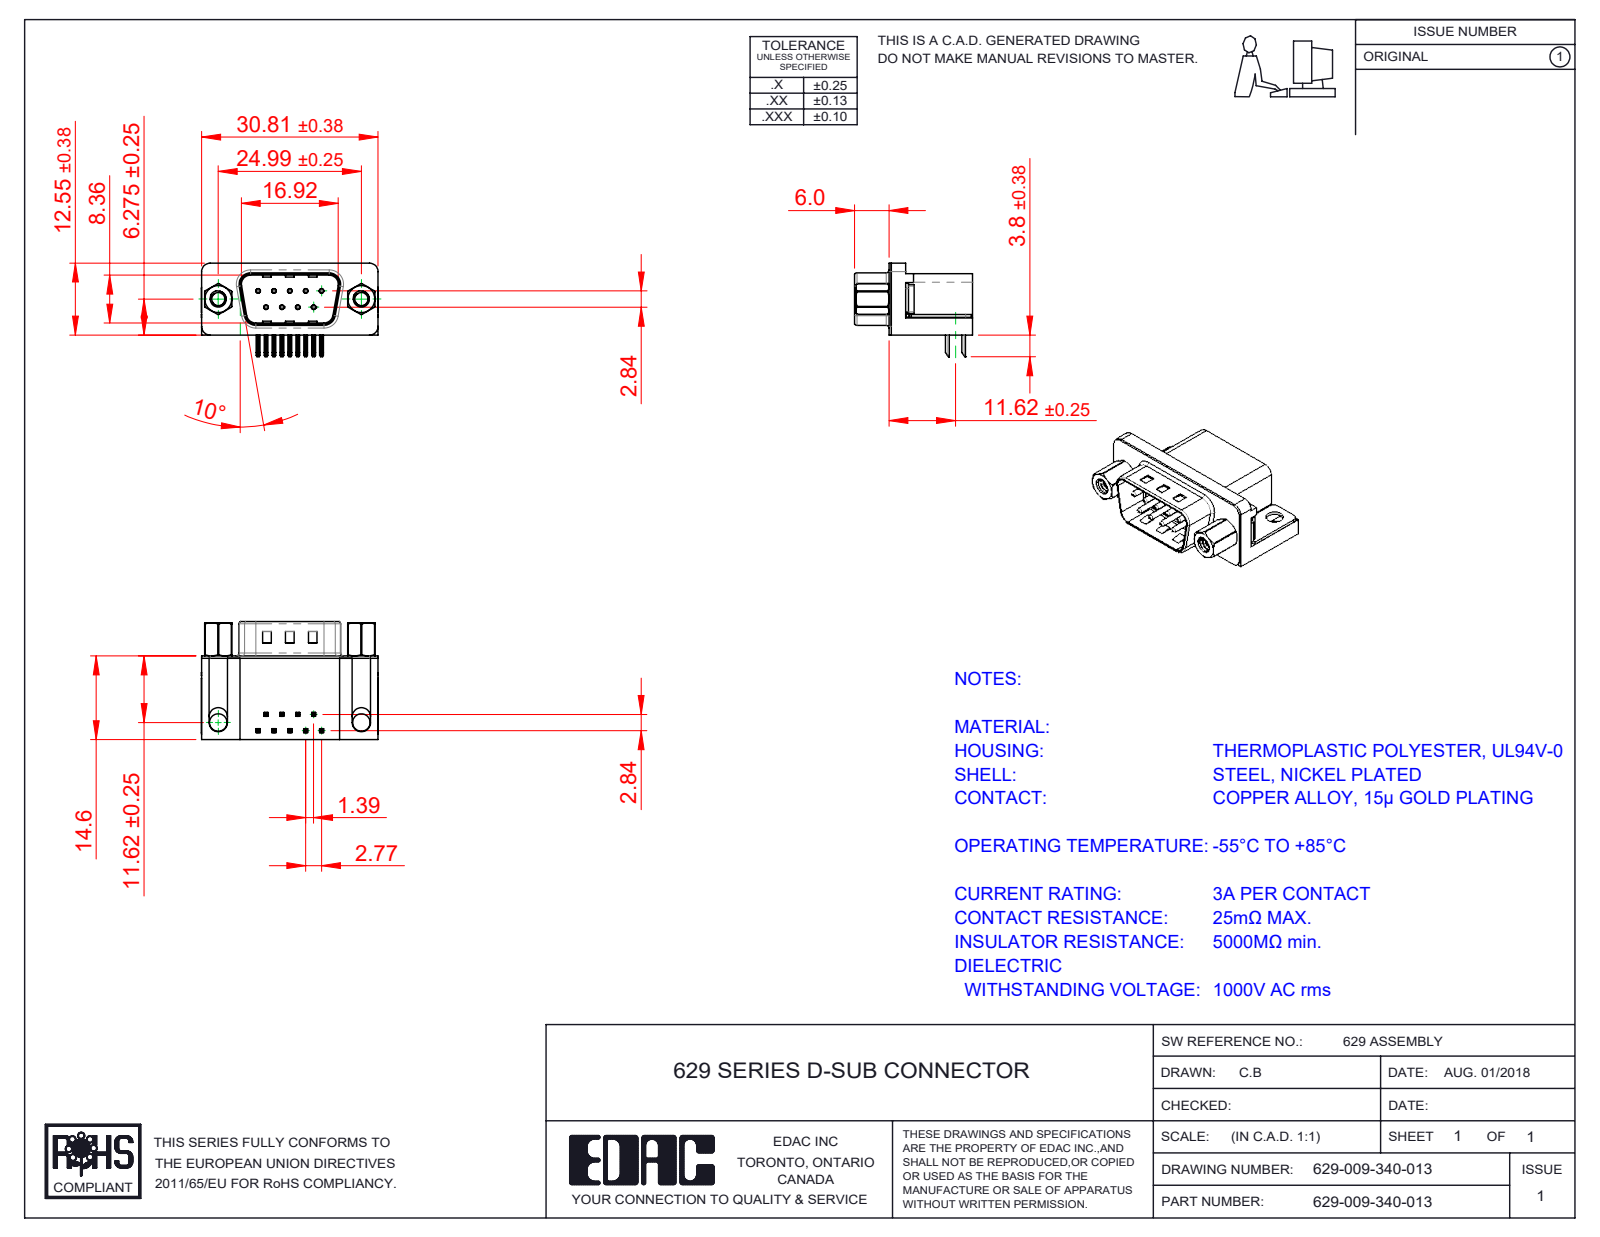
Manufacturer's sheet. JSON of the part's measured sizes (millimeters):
{"part_name": "629 Housing_09 Socket; 629 4-40 Hex Standoff 5; 629 Shell_09 Socket; 629 4-40 Threaded Rivet (+4 more)", "step_written_by": "SolidWorks 2020 (CONFIG_CONTROL_DESIGN)", "units": "millimeters", "bodies": {"solids": 17, "faces": 1115, "planar": 593, "cylindrical": 387, "other": 135}, "overall_size": [30.89, 20.6, 16.35], "volume_mm3": 3930, "surface_area_mm2": 5210, "round_holes": [[0.35, 9], [0.8, 9], [2.26, 2], [2.29, 2], [3.05, 2], [4, 2], [4.8, 2], [5, 2]], "round_bosses_or_shafts": [[0.75, 9], [4.9, 2], [4.75, 2], [3.9, 2], [2.79, 2]], "partial_cylinders_radius": [[0.25, 44], [0.12, 18], [1, 16], [0.5, 9], [1.5, 8], [1.6, 8], [0.9, 4], [2, 4]], "face_to_face_distances": [0.4, 14.2, 14.6, 10.35, 0.5, 11.7, 2.5, 2.9, 2.1, 6.7], "hole_center_spacings": [3.16, 2.77, 5.54, 5.03, 5.04, 8.31, 7.48, 7.49]}
